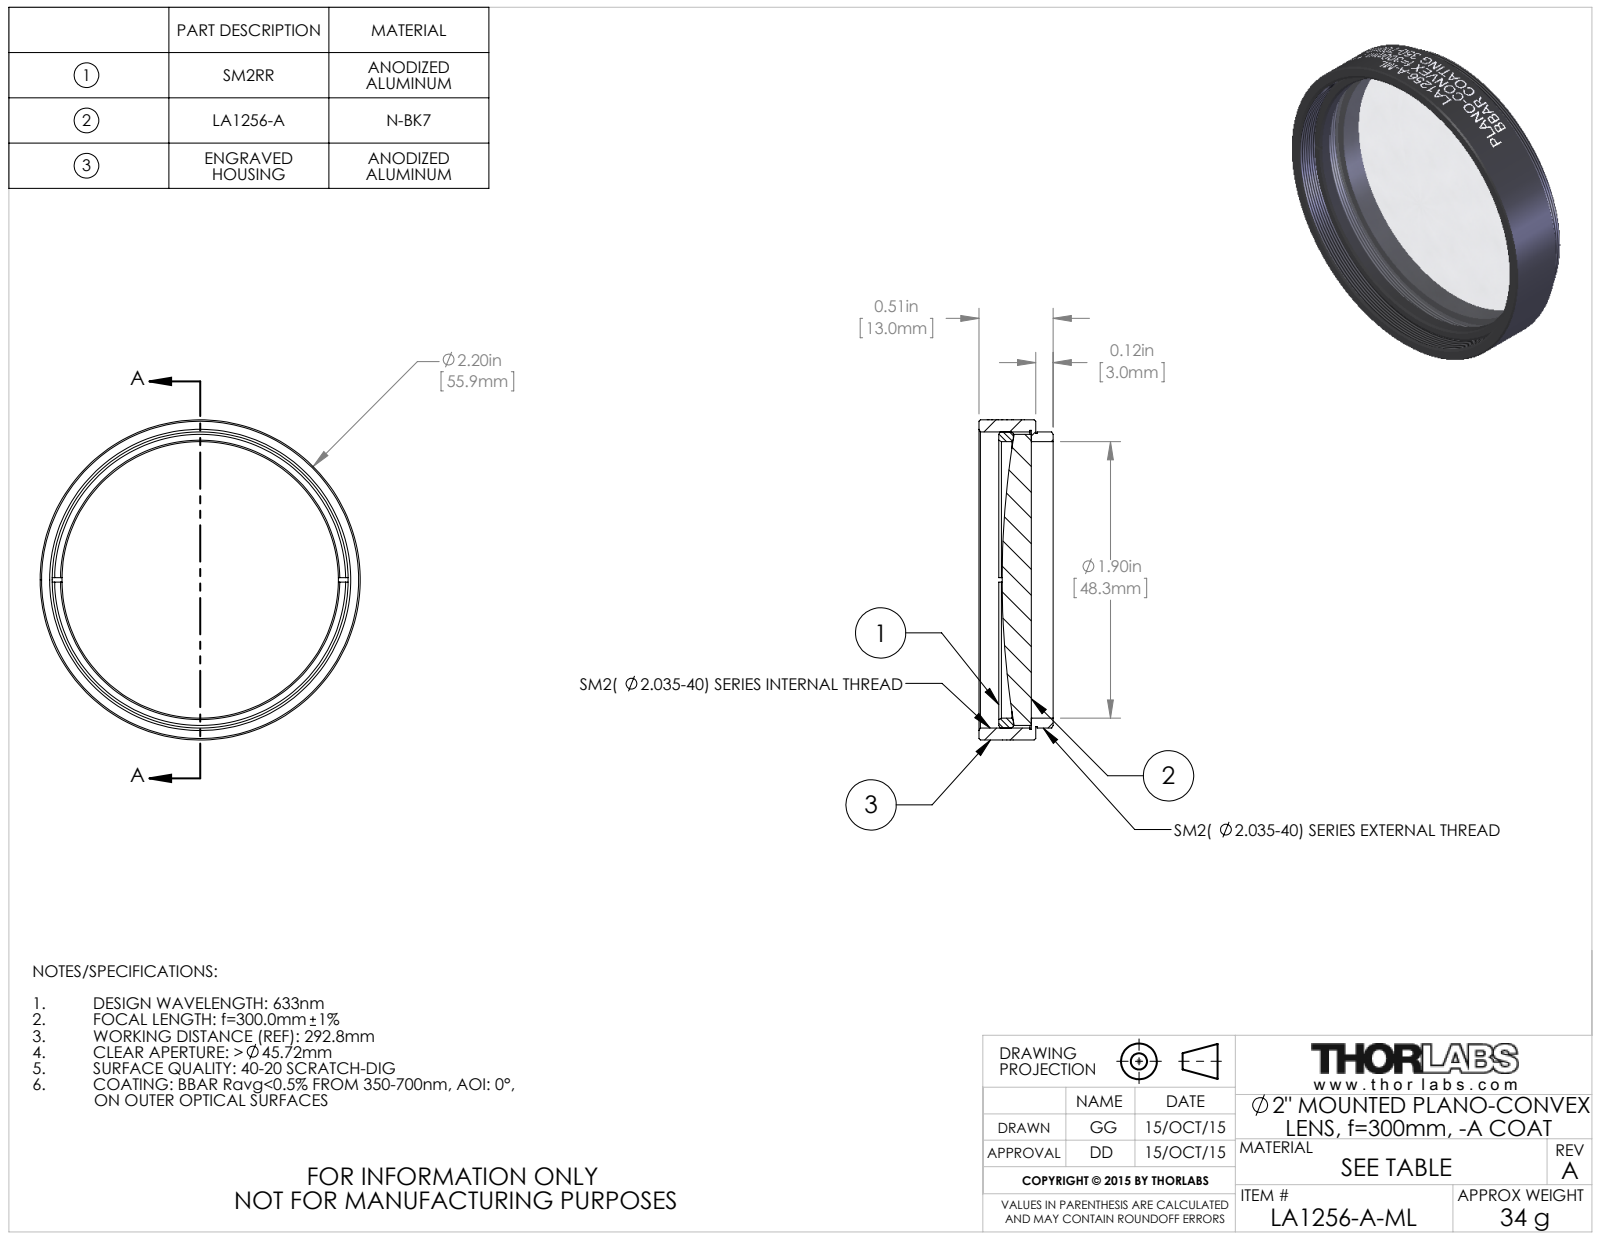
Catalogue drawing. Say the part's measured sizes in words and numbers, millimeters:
The part is named "TTN039535-E0W". Its 3-D file was written by "SolidWorks 2014 (CONFIG_CONTROL_DESIGN)". It is 3 solids with 142 faces: 16 planar, 106 cylindrical and 20 other. Overall it measures 55.9 by 55.9 by 13 millimeters. Its volume is 13 300 cubic millimeters and its surface area 11 360 square millimeters. Round holes: 1 of diameter 48.3, 1 of diameter 52.2. Round bosses or shafts: 1 of diameter 55.9, 1 of diameter 51.7, 1 of diameter 51.2, 1 of diameter 50.8. The main face-to-face distances are 0.8, 9.9, 9.1, 3, 3.8, 13, 7, 3.9, 3.1, 6.
